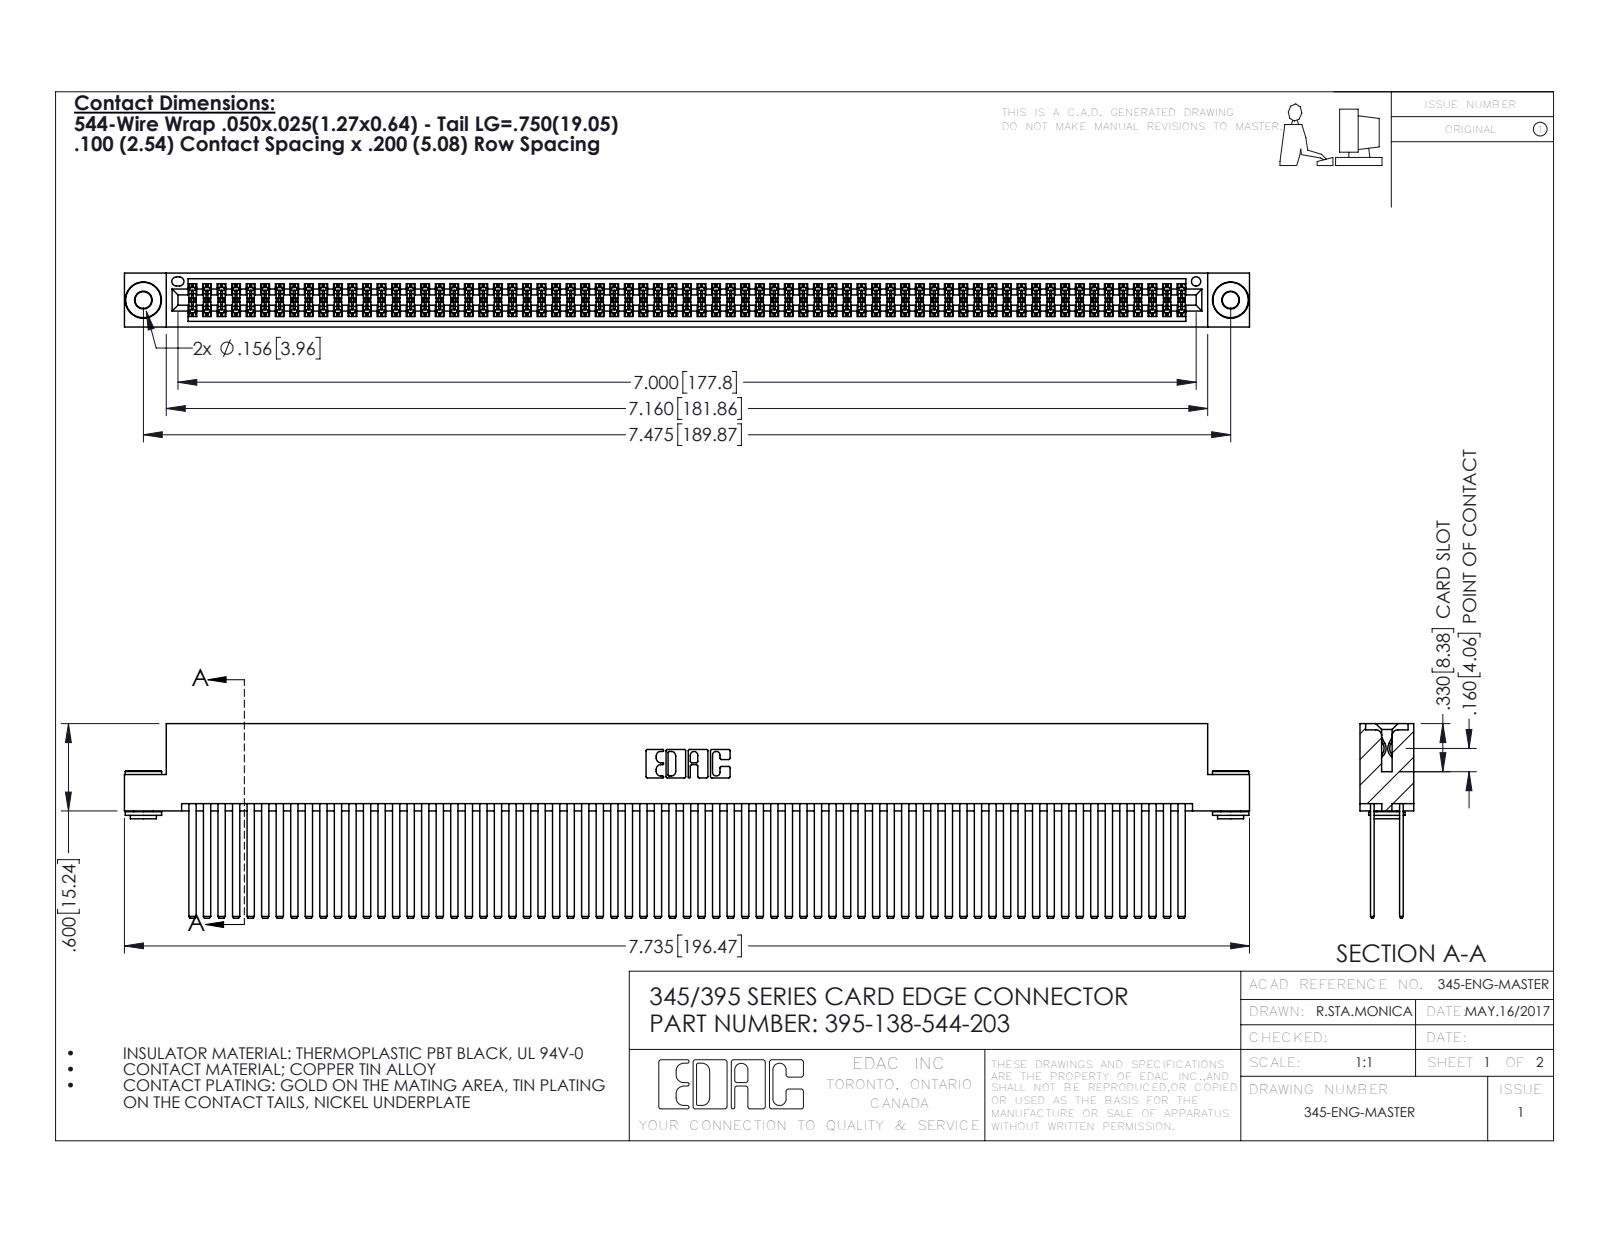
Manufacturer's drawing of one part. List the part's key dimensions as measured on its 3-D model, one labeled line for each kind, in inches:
Part name (STEP PRODUCT): 345-250-002_345-250-002-102; 345 Part_Flush Mounting Lugs - 0.156 Dia-TH; 395-138-544-203; 345-292-001_345-293-144
STEP written by: SolidWorks 2016 (CONFIG_CONTROL_DESIGN)
Units: inches
Bodies: 141 solids, 6236 faces (4092 planar, 2136 cylindrical, 8 other)
Overall size (bounding box): 7.735 × 1.337 × 0.37
Volume: 1.299 in³ · Surface area: 58.69 in²
Round holes (diameter × count): ⌀0.116 ×2, ⌀0.156 ×2, ⌀0.064 ×1
Round bosses / shafts (diameter × count): ⌀0.25 ×2, ⌀0.18 ×2, ⌀0.136 ×2
Partial cylindrical surfaces — rounded edges, fillets, slot ends (radius × count): R0.006 ×207, R0.01 ×22, R0.007 ×6, R0.031 ×6, R0.026 ×3, R0.014 ×2, R0.019 ×2, R0.022 ×2
Main face-to-face distances: 0.2, 0.025, 0.072, 0.098, 0.272, 0.298, 0.225, 0.175, 0.37, 0.05
Hole centre spacings: 0.27, 7.239, 7.475
